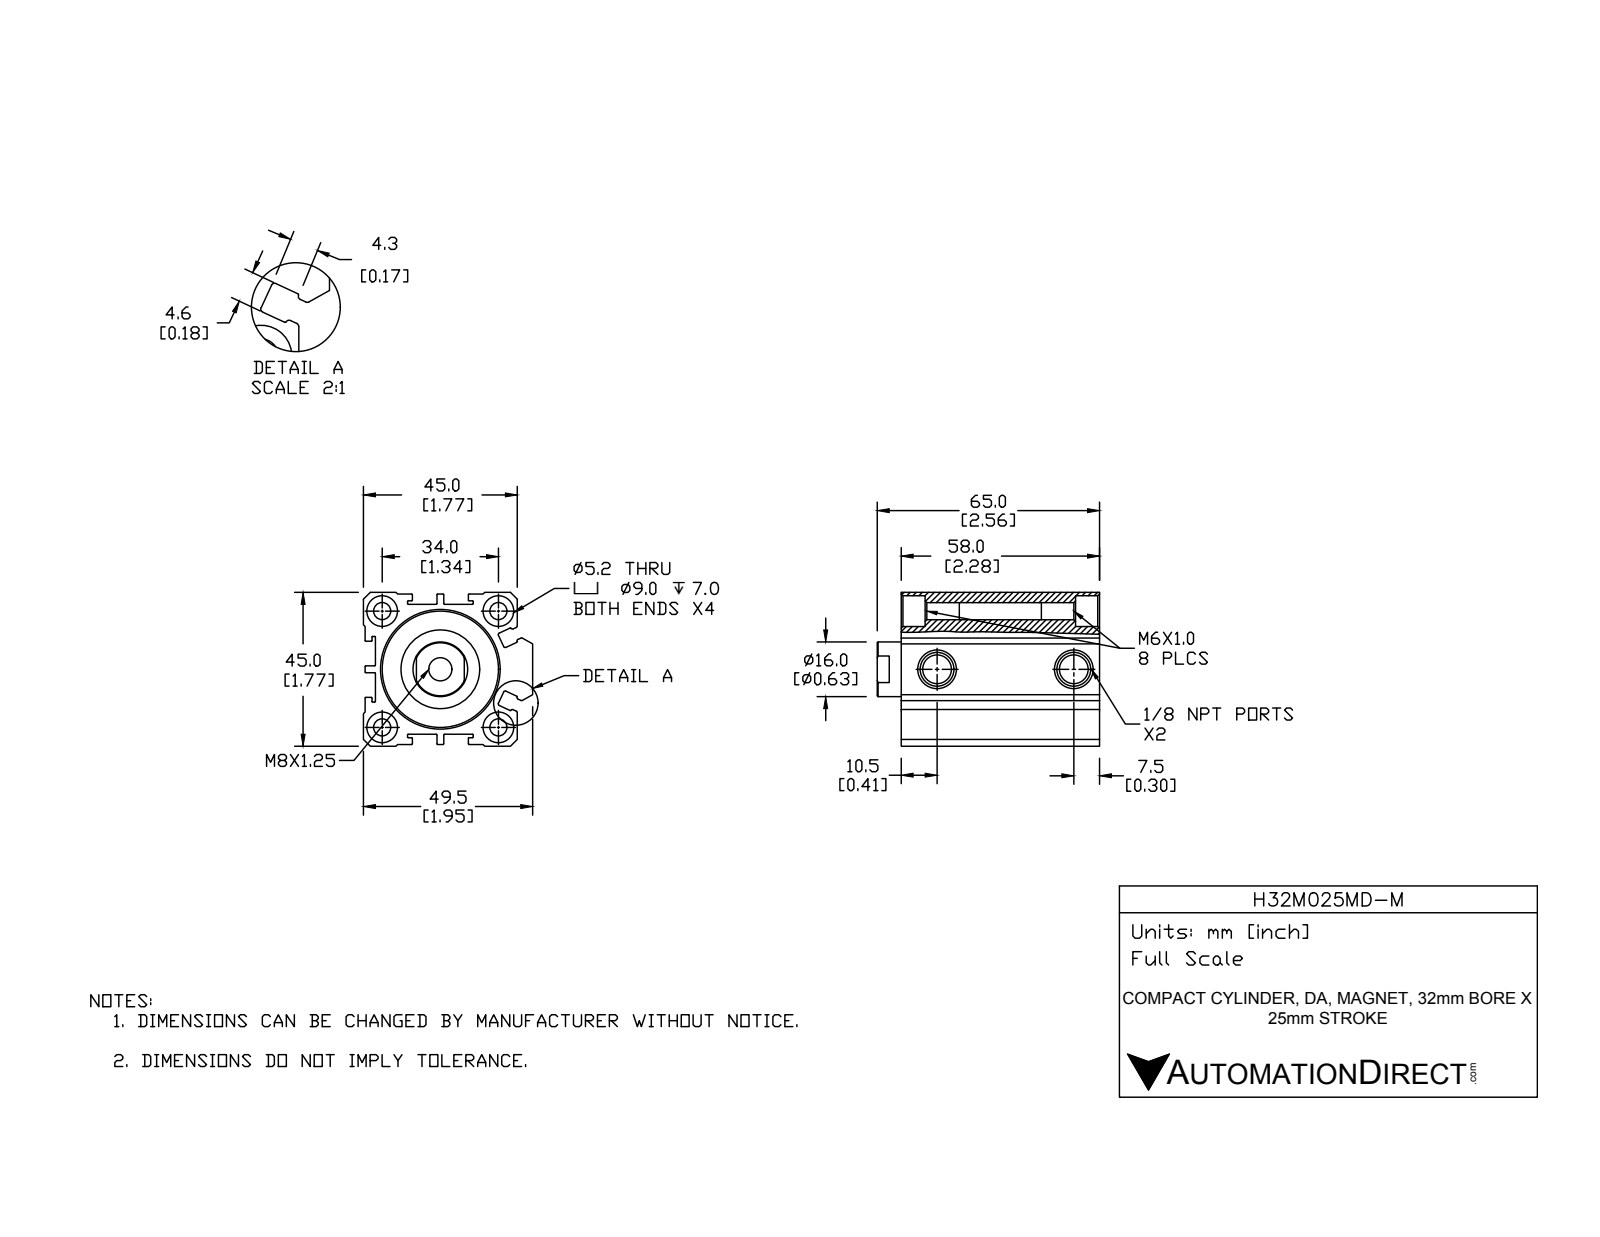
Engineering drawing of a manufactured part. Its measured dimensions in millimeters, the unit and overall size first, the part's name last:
Units: millimetres
Overall size (bounding box): 65 × 49.5 × 45
Round holes (diameter × count): ⌀5 ×4, ⌀9 ×4, ⌀8.43 ×2, ⌀6.8 ×1, ⌀16 ×1, ⌀23 ×1, ⌀28 ×1, ⌀32 ×1, ⌀34 ×1
Round bosses / shafts (diameter × count): ⌀20 ×1
Partial cylindrical surfaces — rounded edges, fillets, slot ends (radius × count): R0.2 ×40, R0.5 ×12
Main face-to-face distances: 3.5, 41.5, 3, 45, 44.5, 0.5, 4.5, 41, 46, 38
Hole centre spacings: 24.04, 34, 48.08, 40
Volume: 82 691 mm³ · Surface area: 35 774 mm²
Bodies: 2 solids, 255 faces (99 planar, 103 cylindrical, 53 other)
Part name (STEP PRODUCT): H32M025MD-M; H32M025MD-M-BODY; H32M025MD-M-PISTON
STEP written by: SolidWorks 2015 (CONFIG_CONTROL_DESIGN)
